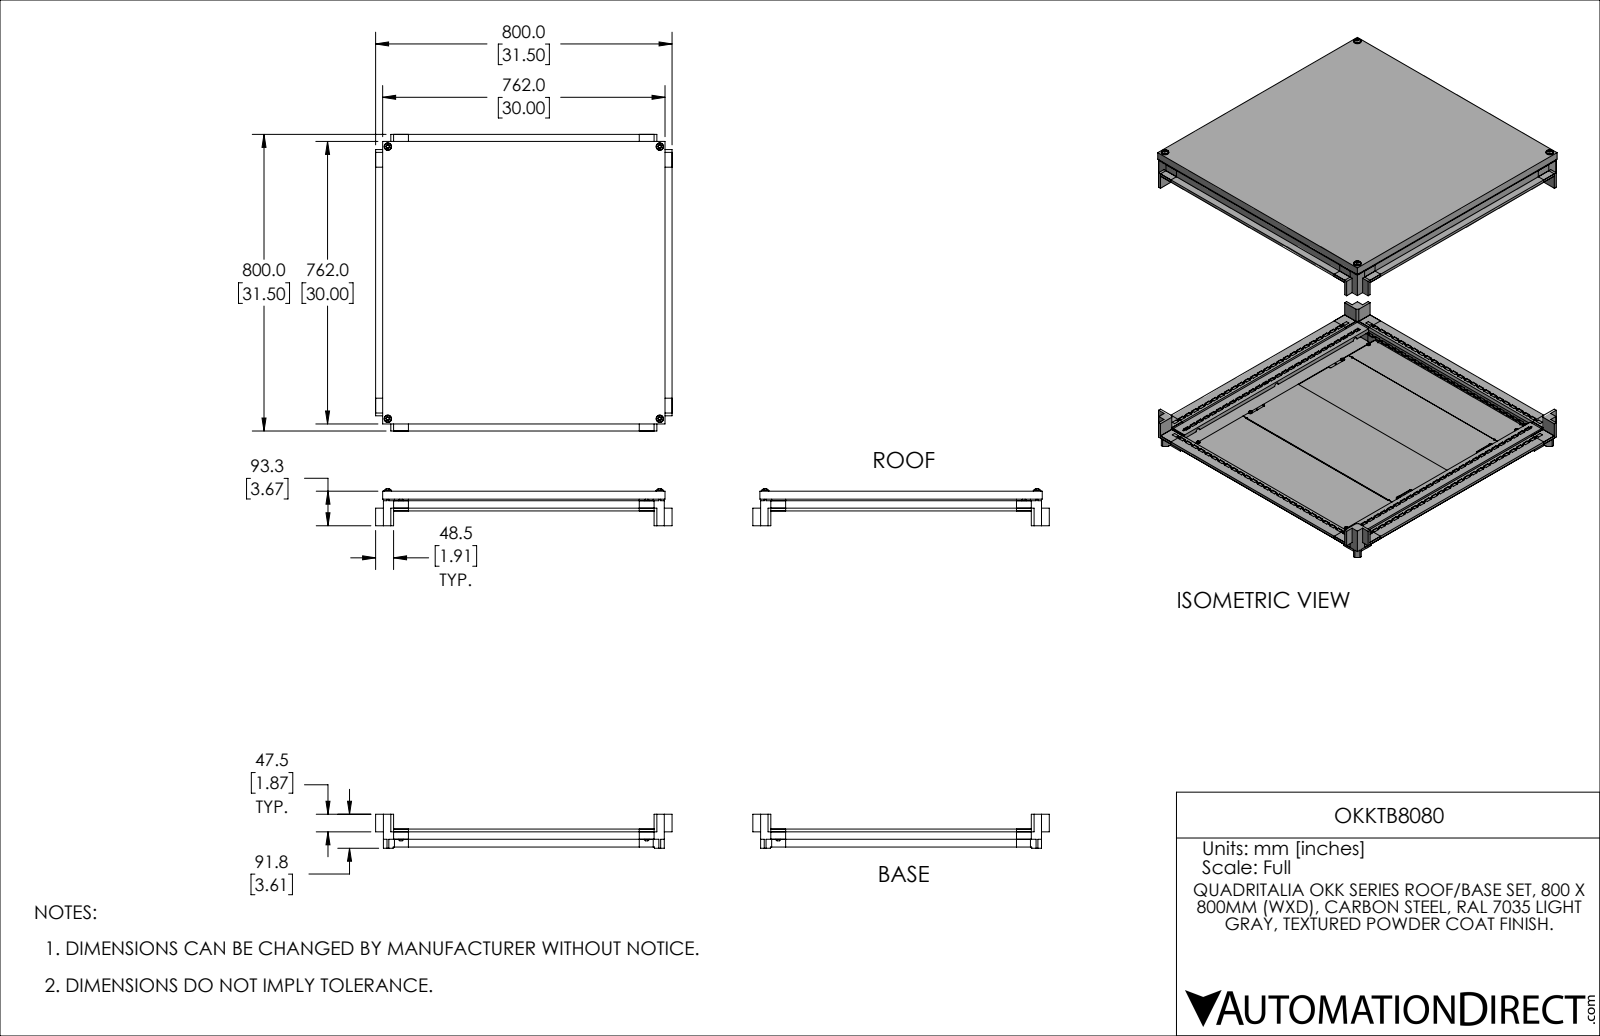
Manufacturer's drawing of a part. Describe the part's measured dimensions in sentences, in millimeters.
The part is named "OKKTB8080". Its 3-D file was written by "SolidWorks 2021 (AUTOMOTIVE_DESIGN)". It is 62 solids with 5231 faces: 4038 planar, 1022 cylindrical and 171 other. Overall it measures 969.2 by 800 by 800 millimeters. Its volume is 9 580 000 cubic millimeters and its surface area 4 159 000 square millimeters. Round holes: 316 of diameter 4.2, 11 of diameter 9, 8 of diameter 3.9, 4 of diameter 13.5, 3 of diameter 4.9, 3 of diameter 8.2. Round bosses or shafts: 11 of diameter 14, 11 of diameter 10, 11 of diameter 8, 8 of diameter 5, 4 of diameter 20, 4 of diameter 12, 4 of diameter 6, 1 of diameter 7. Partial cylindrical surfaces (rounded edges, fillets, slot ends): 264 of radius 0.5, 24 of radius 1, 16 of radius 0.3, 12 of radius 3.5, 12 of radius 4.5, 6 of radius 5.5, 3 of radius 7, 1 of radius 0.8. The main face-to-face distances are 1.5, 936.2, 937.7, 20, 2.5, 27.5, 7.5, 28, 934.7, 17.5. The hole center spacings are 25, 50, 75, 100, 125, 150, 175, 200.
